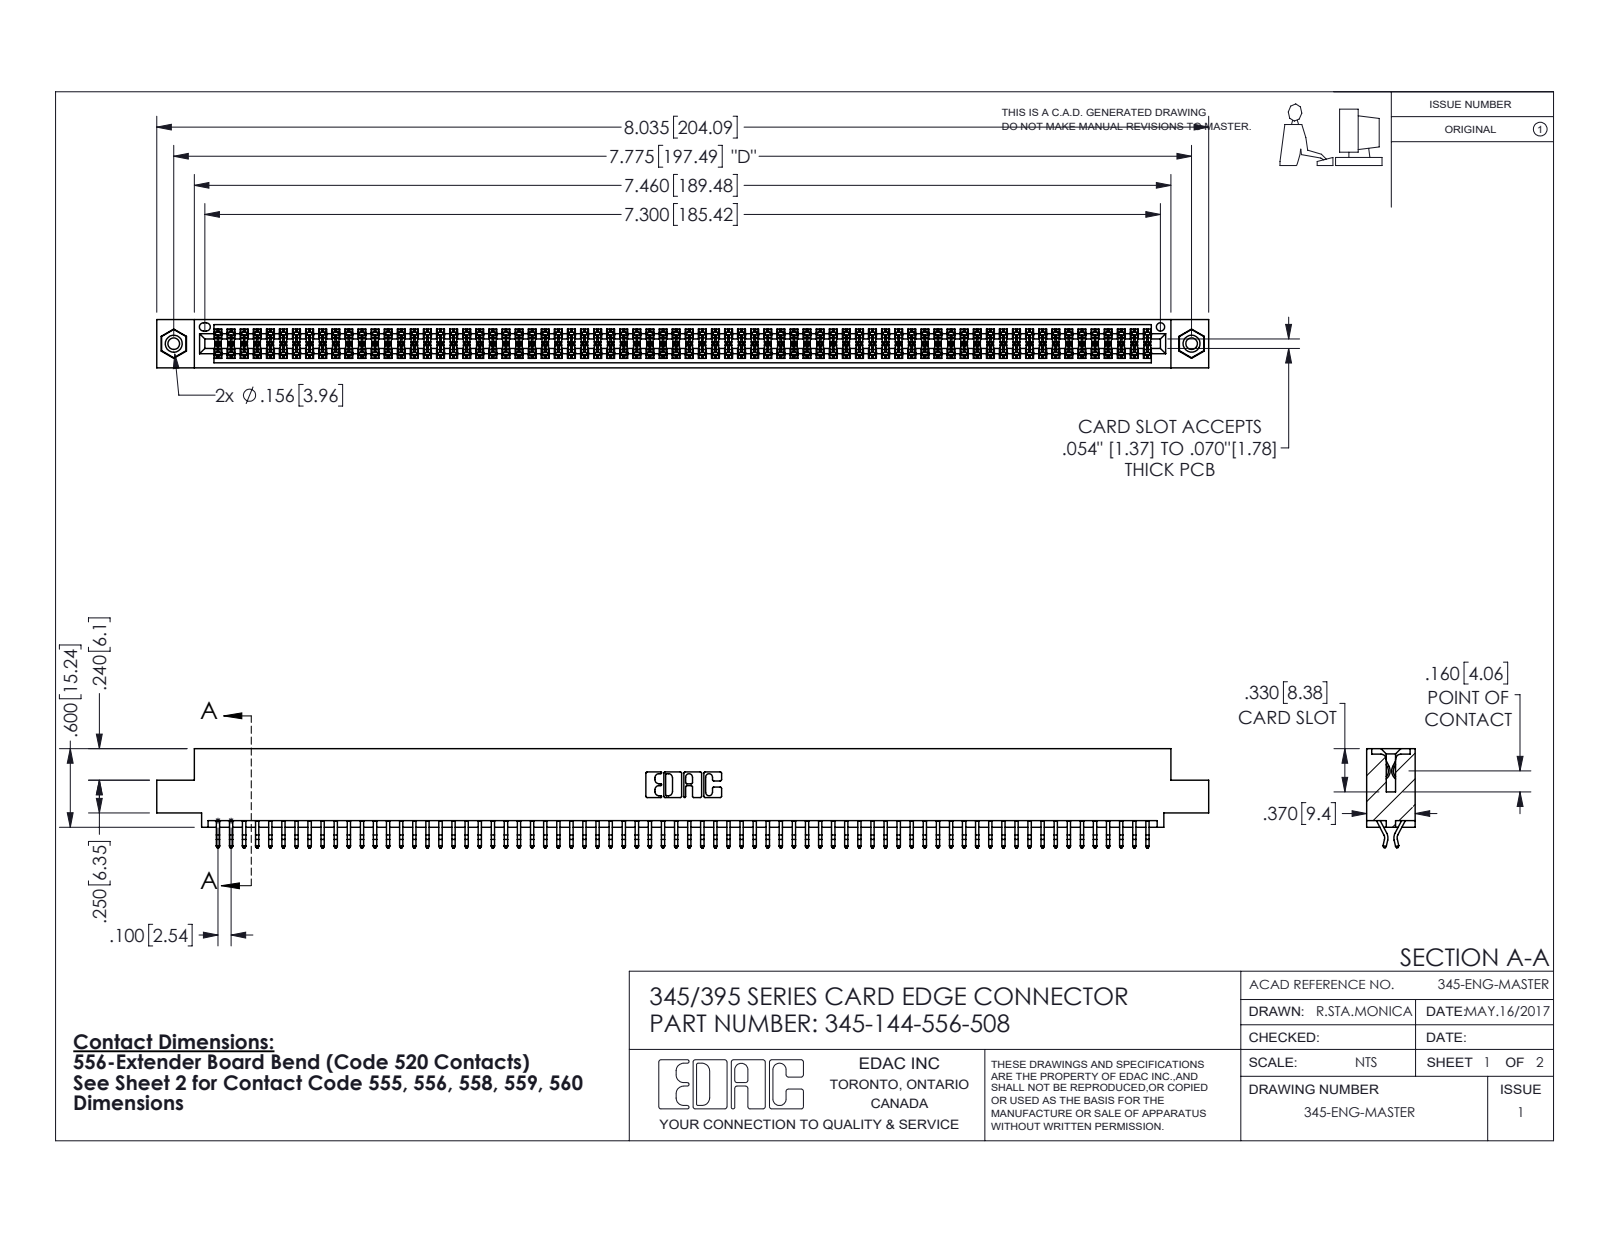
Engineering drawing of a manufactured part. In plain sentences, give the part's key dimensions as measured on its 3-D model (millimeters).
The part is named "345-250-001_345-250-003-102; 345 Part_0.110 Offset - 0.156 Dia-TI; 345-144-556-508; 345-292-001_556 Tail". Its 3-D file was written by "SolidWorks 2016 (CONFIG_CONTROL_DESIGN)". It is 147 solids with 8254 faces: 5444 planar, 2794 cylindrical and 16 other. Overall it measures 204.1 by 19.2 by 9.4 millimeters. Its volume is 20 020 cubic millimeters and its surface area 30 150 square millimeters. Round holes: 2 of diameter 2.3, 2 of diameter 3.2, 2 of diameter 4, 1 of diameter 1.6. Round bosses or shafts: 2 of diameter 3.9. Partial cylindrical surfaces (rounded edges, fillets, slot ends): 216 of radius 0.2, 22 of radius 0.3, 6 of radius 0.2, 6 of radius 0.8, 3 of radius 0.7, 2 of radius 0.3, 2 of radius 0.4, 2 of radius 0.5. The main face-to-face distances are 1.8, 7.6, 9.4, 5.1, 0.6, 2.5, 6.9, 5.7, 4.4, 3.8. The hole center spacings are 6.9, 191.5, 197.5.
